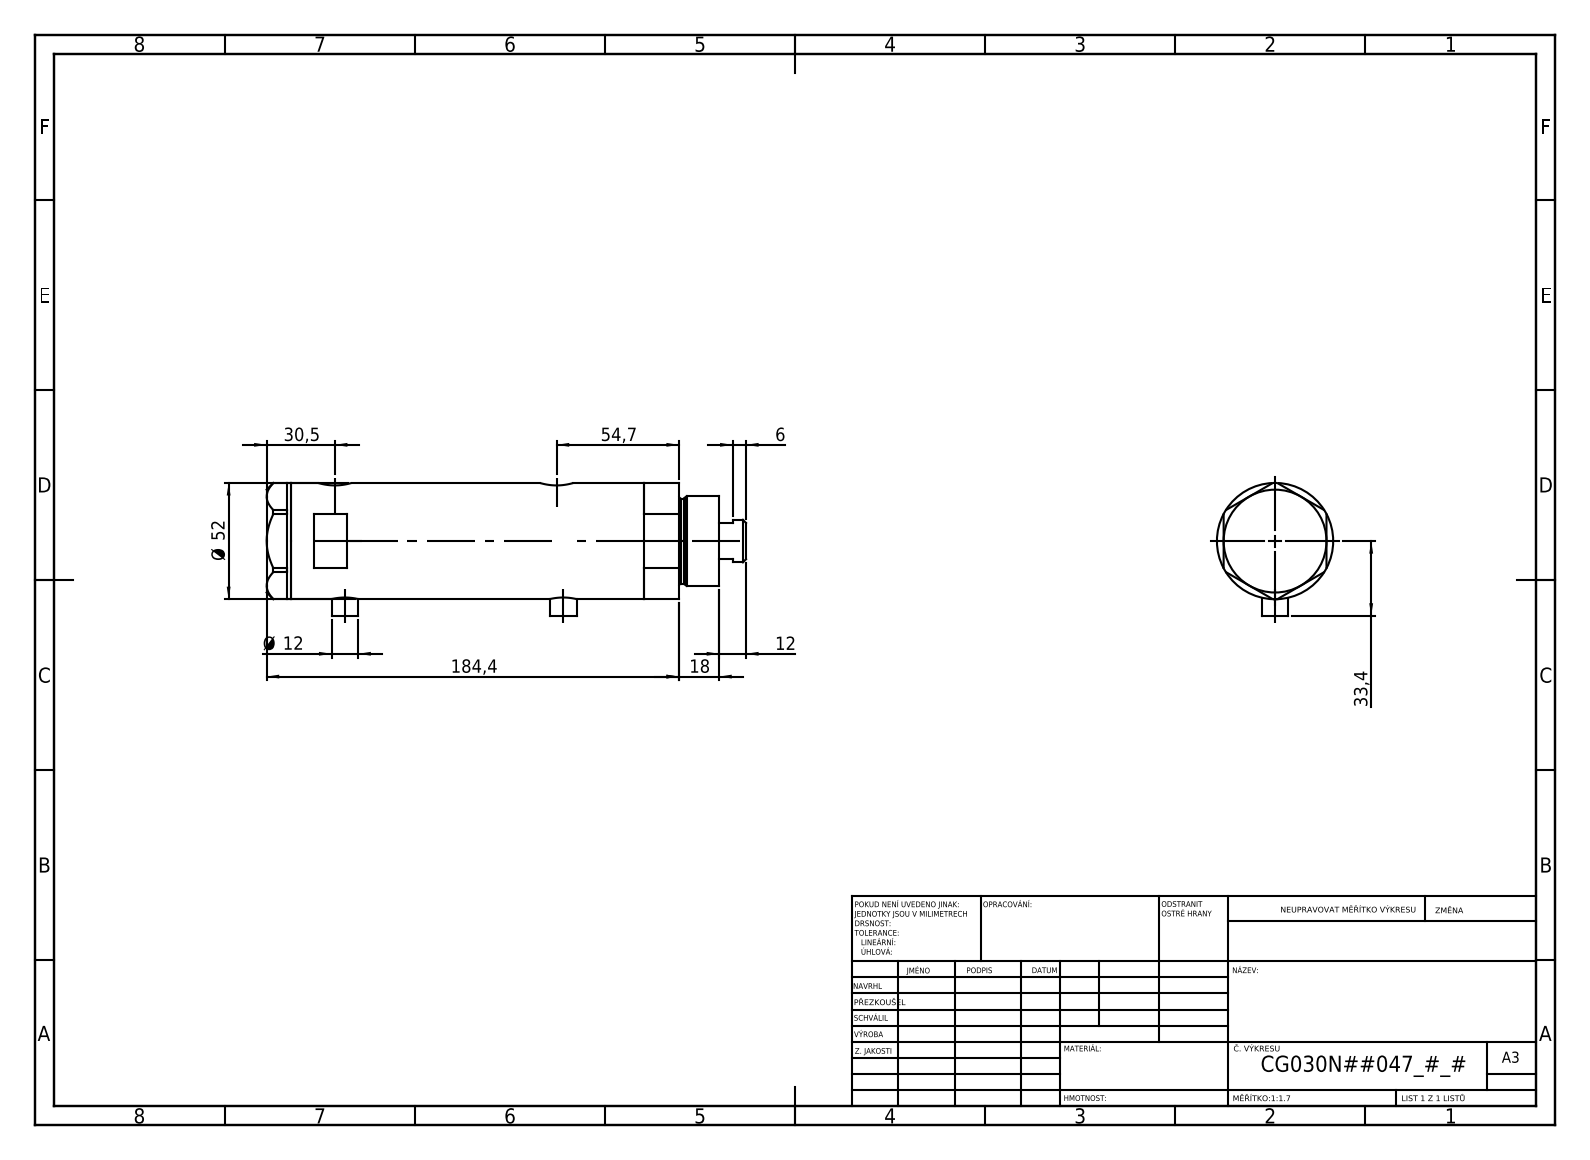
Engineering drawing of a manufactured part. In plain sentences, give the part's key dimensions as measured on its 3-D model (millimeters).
The part is named "V270CG_VC; V270CG_BACK; V270CG_FRONT; V270CG_MIDDLE". Its 3-D file was written by "SolidWorks 2019 (CONFIG_CONTROL_DESIGN)". It is 4 solids with 134 faces: 65 planar, 49 cylindrical and 20 other. Overall it measures 214.4 by 59.4 by 52 millimeters. Its volume is 391 955 cubic millimeters and its surface area 87 156 square millimeters. Round holes: 2 of diameter 9.73, 2 of diameter 12.5, 2 of diameter 15, 1 of diameter 6.5, 1 of diameter 20, 1 of diameter 21.5, 1 of diameter 30, 1 of diameter 33, 1 of diameter 44. Round bosses or shafts: 2 of diameter 12, 1 of diameter 52, 1 of diameter 40, 1 of diameter 38, 1 of diameter 19. The main face-to-face distances are 121.5, 23.8, 97.7, 11, 34.8, 132.5, 46, 168.9, 157.9, 134.1. The hole center spacings are 2.9, 4.5, 94.7, 97.6, 99.2, 102.1.
